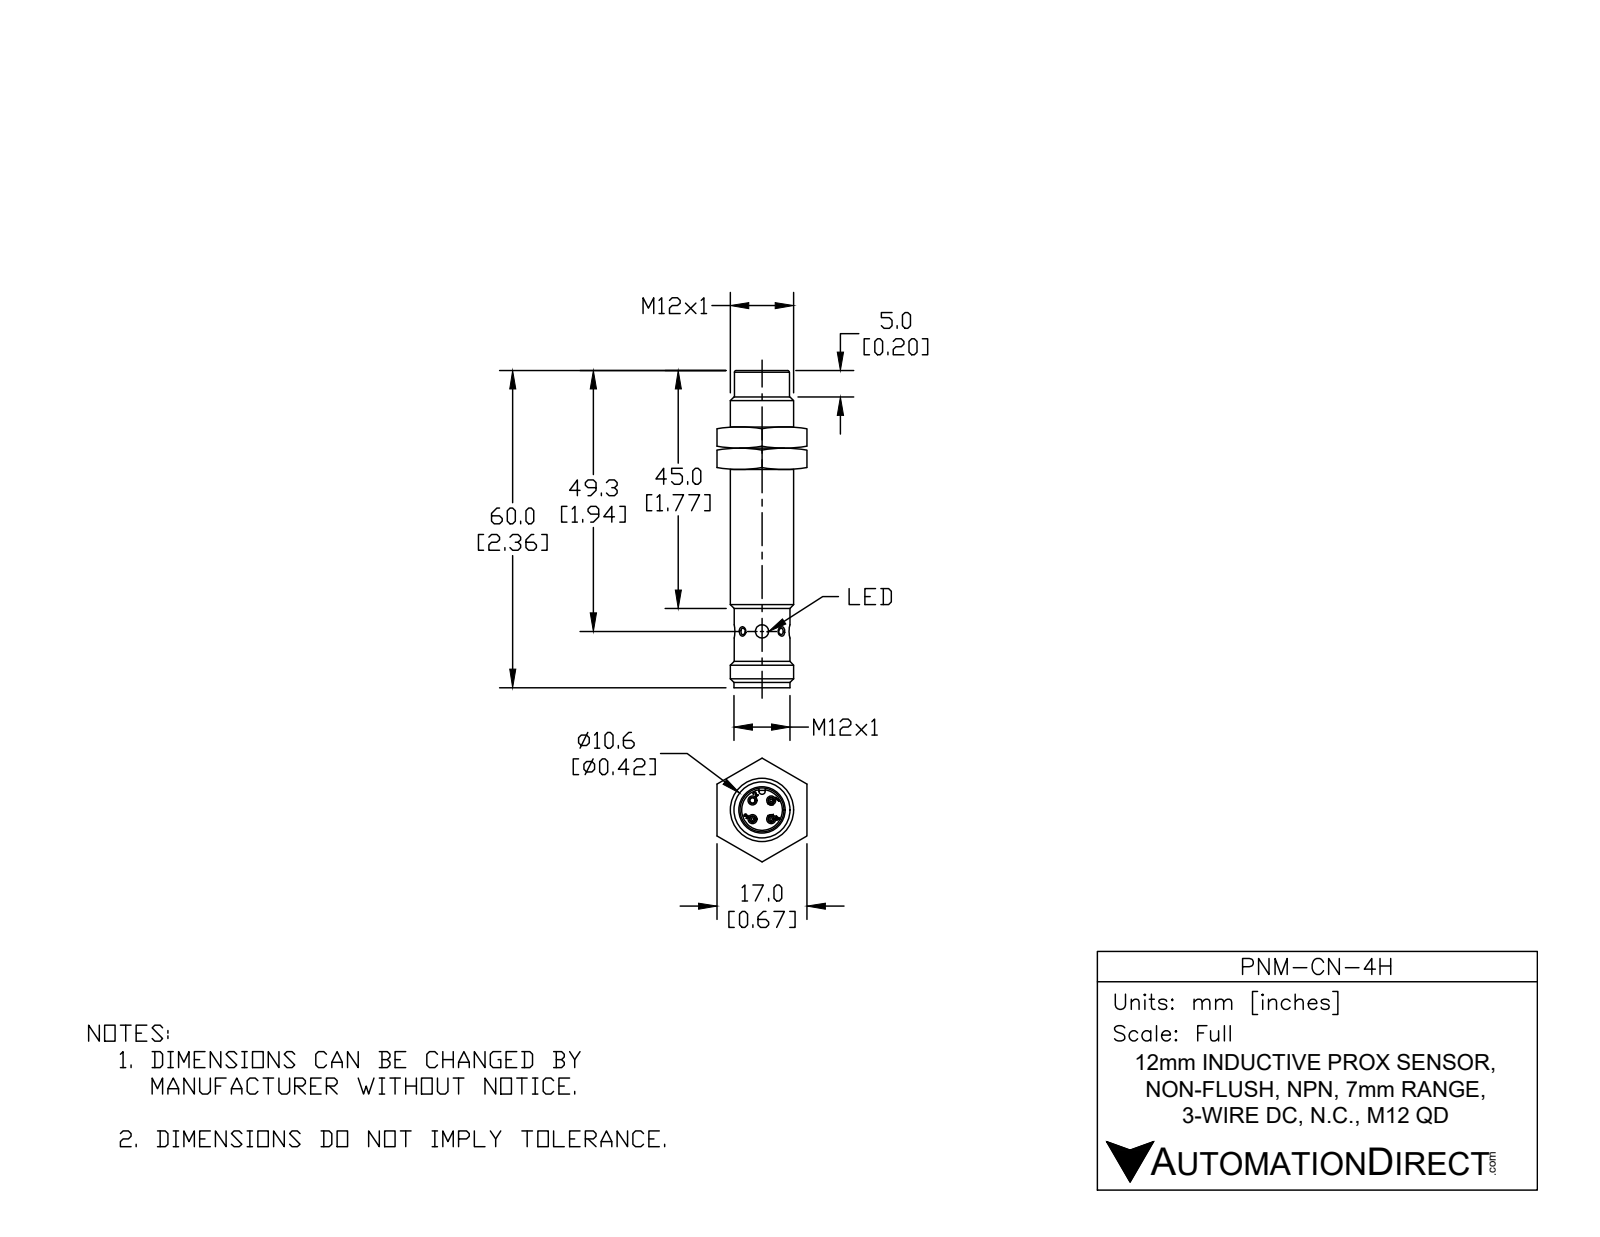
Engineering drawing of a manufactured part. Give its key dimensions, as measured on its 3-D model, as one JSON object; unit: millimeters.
{"part_name": "PNM-CN-4H", "step_written_by": "SolidWorks 2017 (AUTOMOTIVE_DESIGN)", "units": "millimeters", "bodies": {"solids": 1, "faces": 479, "planar": 119, "cylindrical": 134, "other": 226}, "overall_size": [60, 12, 12], "volume_mm3": 5740, "surface_area_mm2": 6613, "round_holes": [[1.1, 3], [1, 2], [2.5, 2], [1, 1], [1, 1], [8.3, 1], [10, 1], [10.2, 1]], "round_bosses_or_shafts": [[1, 9], [12, 1], [10.6, 1], [10.5, 1], [10.2, 1], [10, 1], [9.9, 1], [9.6, 1]], "partial_cylinders_radius": [[0.1, 36], [0.6, 1], [0.8, 1], [4.1, 1]], "face_to_face_distances": [1, 47.5, 46.5, 0.5, 0.6, 47, 59, 3.6, 51.1, 50.6], "hole_center_spacings": [2.5, 3.5, 5]}
